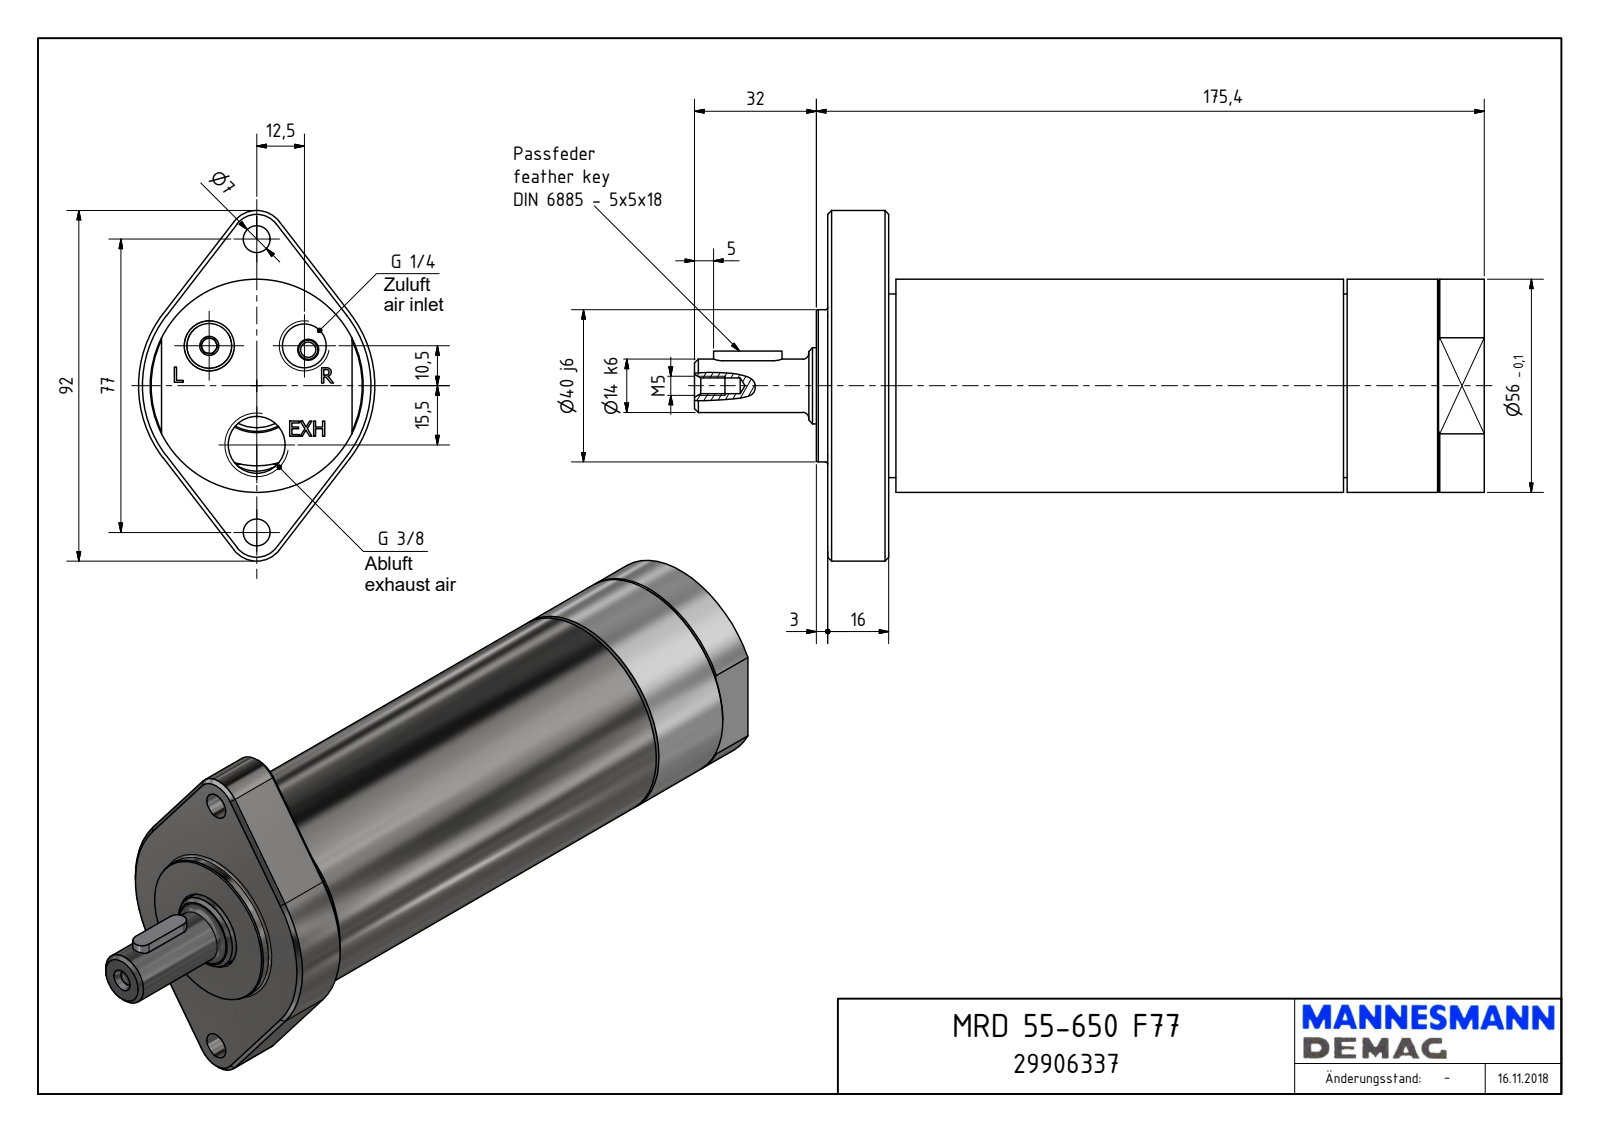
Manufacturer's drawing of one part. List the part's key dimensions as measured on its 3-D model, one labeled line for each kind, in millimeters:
Part name (STEP PRODUCT): MRD 55-650 F77_29906337
STEP written by: Autodesk Inventor 2018 (AUTOMOTIVE_DESIGN)
Units: millimetres
Bodies: 1 solid, 195 faces (112 planar, 29 cylindrical, 54 other)
Overall size (bounding box): 207.4 × 92 × 62
Volume: 445 866 mm³ · Surface area: 46 685 mm²
Round holes (diameter × count): ⌀7 ×2, ⌀4 ×1, ⌀4.13 ×1, ⌀11.45 ×1, ⌀14.95 ×1, ⌀21 ×1, ⌀21.25 ×1, ⌀23.54 ×1, ⌀26 ×1, ⌀48.38 ×1
Round bosses / shafts (diameter × count): ⌀56 ×1, ⌀48.18 ×1, ⌀40 ×1, ⌀19.95 ×1, ⌀14 ×1
Partial cylindrical surfaces — rounded edges, fillets, slot ends (radius × count): R2.5 ×2, R7.5 ×2, R31 ×1
Main face-to-face distances: 172.4, 16, 156.4, 3, 19, 175.4, 20.9, 17.9, 1.9, 154.5
Hole centre spacings: 16.32, 28.85, 30.66, 38.5, 50.57, 15.5, 23, 25
